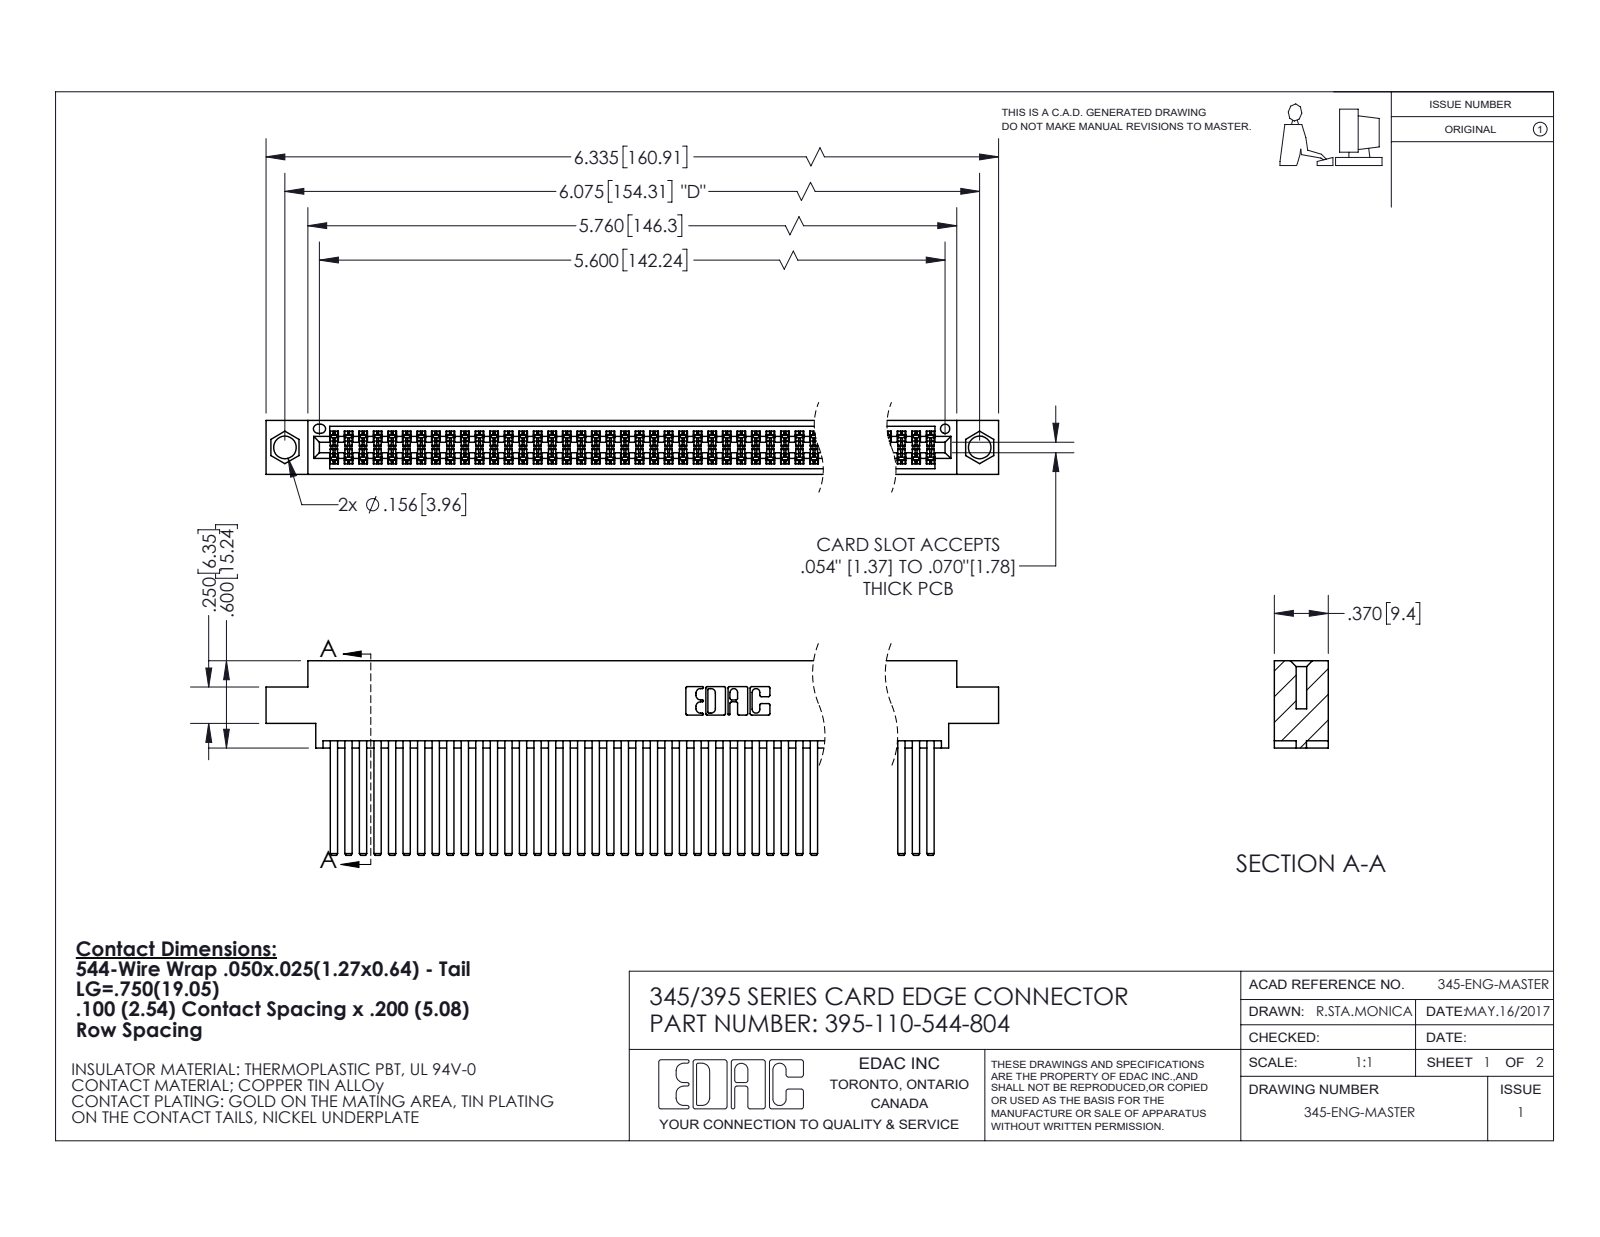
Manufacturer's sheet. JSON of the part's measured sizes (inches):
{"part_name": "345 Part_0.170 Offset - 0.156 Dia-TI; 345-292-001_345-293-144; 395-110-544-804", "step_written_by": "SolidWorks 2020 (CONFIG_CONTROL_DESIGN)", "units": "inches", "bodies": {"solids": 111, "faces": 4984, "planar": 3288, "cylindrical": 1696, "other": 0}, "overall_size": [6.335, 1.337, 0.37], "volume_in3": 1.042, "surface_area_in2": 46.51, "round_holes": [[0.156, 2], [0.064, 1]], "partial_cylinders_radius": [[0.006, 220], [0.01, 22], [0.007, 6], [0.031, 6], [0.026, 3], [0.014, 2], [0.019, 2], [0.022, 2]], "face_to_face_distances": [0.2, 0.025, 0.072, 0.098, 0.272, 0.298, 0.225, 0.175, 0.37, 0.15], "hole_center_spacings": [0.27, 5.839, 6.075]}
